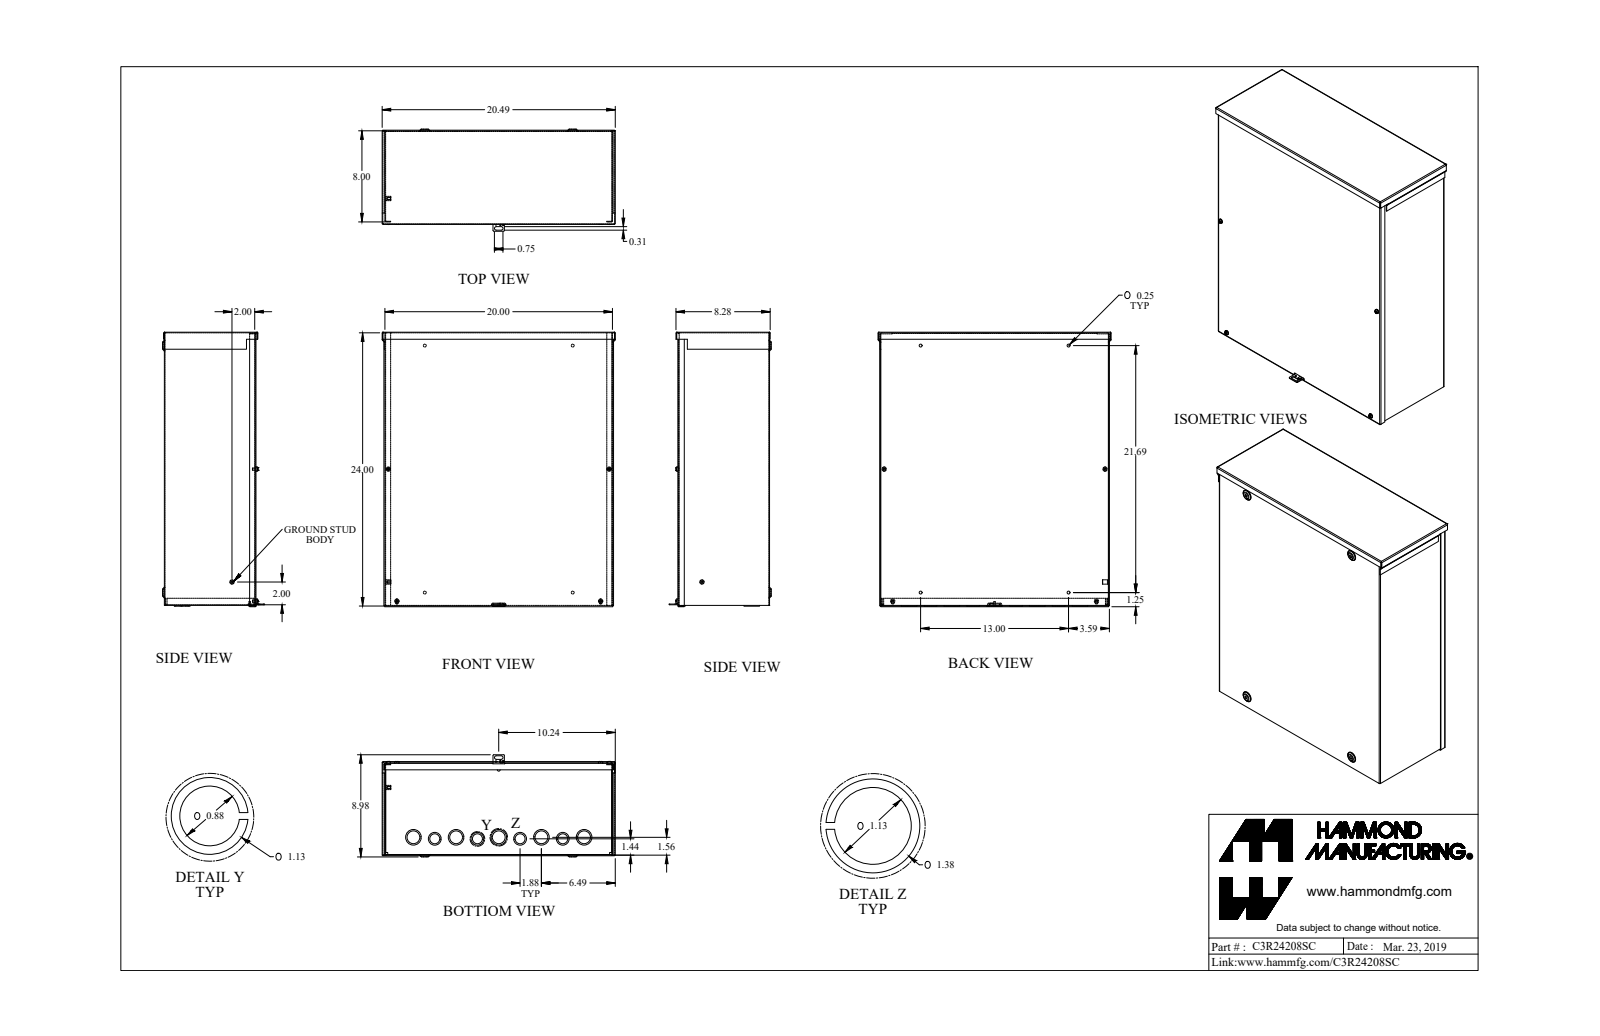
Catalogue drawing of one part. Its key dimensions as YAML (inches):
part_name: "C3R24208SC_Default"
step_written_by: "SolidWorks 2019 (CONFIG_CONTROL_DESIGN)"
units: inches
bodies: {solids: 11, faces: 457, planar: 238, cylindrical: 133, other: 86}
overall_size: [24.12, 20.489, 8.977]
volume: 103.2
surface_area: 3637
round_holes:
  - {diameter: 0.17, count: 4}
  - {diameter: 0.25, count: 4}
  - {diameter: 1.125, count: 3}
  - {diameter: 0.875, count: 2}
  - {diameter: 0.875, count: 2}
  - {diameter: 1.125, count: 2}
  - {diameter: 0.125, count: 1}
  - {diameter: 0.137, count: 1}
  - {diameter: 0.156, count: 1}
round_bosses_or_shafts:
  - {diameter: 1.125, count: 4}
  - {diameter: 0.19, count: 4}
  - {diameter: 1.375, count: 3}
  - {diameter: 0.375, count: 3}
  - {diameter: 1.375, count: 2}
  - {diameter: 0.375, count: 2}
  - {diameter: 0.125, count: 1}
partial_cylinders:
  - {radius: 0.029, count: 21}
  - {radius: 0.086, count: 21}
  - {radius: 0.109, count: 8}
  - {radius: 0.125, count: 8}
  - {radius: 0.156, count: 2}
face_to_face_distances: [0.057, 8, 7.943, 8.057, 19.943, 0.057, 20, 19.886, 23.886, 23.943]
hole_center_spacings: [3.75, 1.879, 1.88, 5.627, 7.5, 11.311, 19.502, 9.376]
